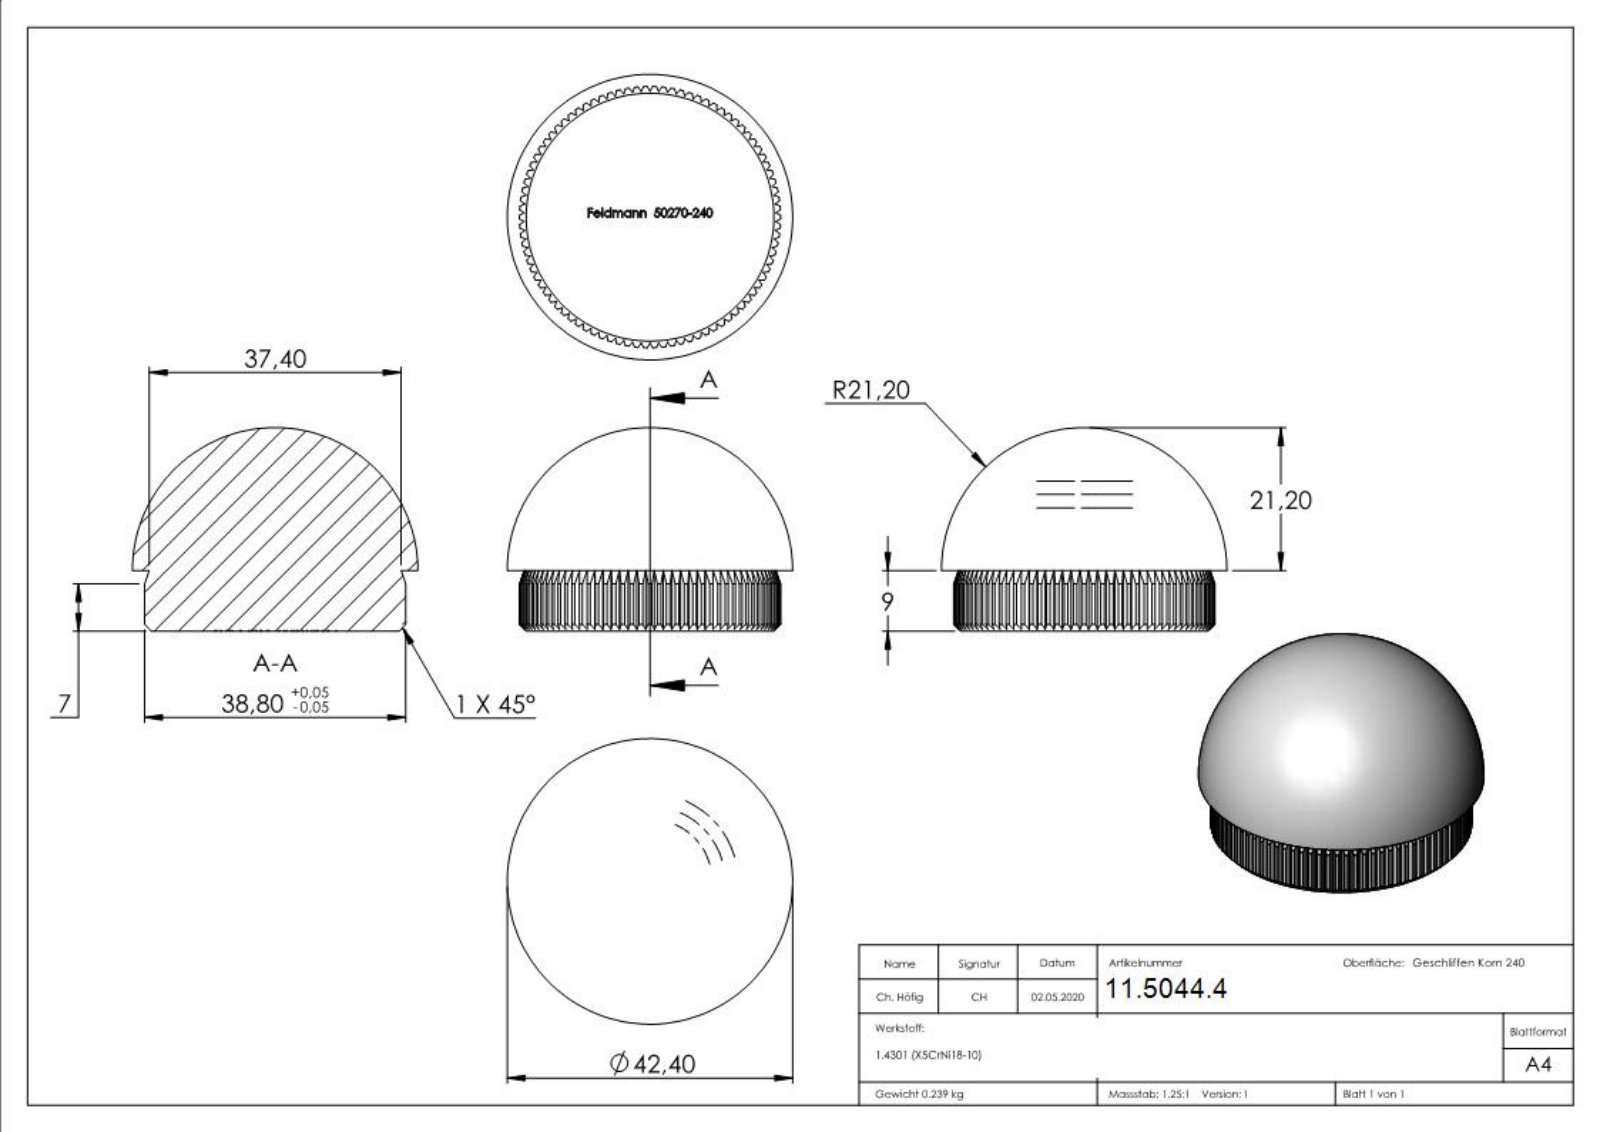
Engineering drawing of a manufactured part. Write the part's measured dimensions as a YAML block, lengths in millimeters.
part_name: "50270-240"
step_written_by: "SolidWorks 2015 (CONFIG_CONTROL_DESIGN)"
units: millimeters
bodies: {solids: 1, faces: 586, planar: 306, cylindrical: 91, other: 189}
overall_size: [42.4, 42.4, 30.2]
volume: 30277
surface_area: 5880
partial_cylinders:
  - {radius: 19.4, count: 1}
face_to_face_distances: [18.7, 9, 18.72, 18.71, 18.68, 18.69, 8.9, 9.35, 1.32, 0.44]
